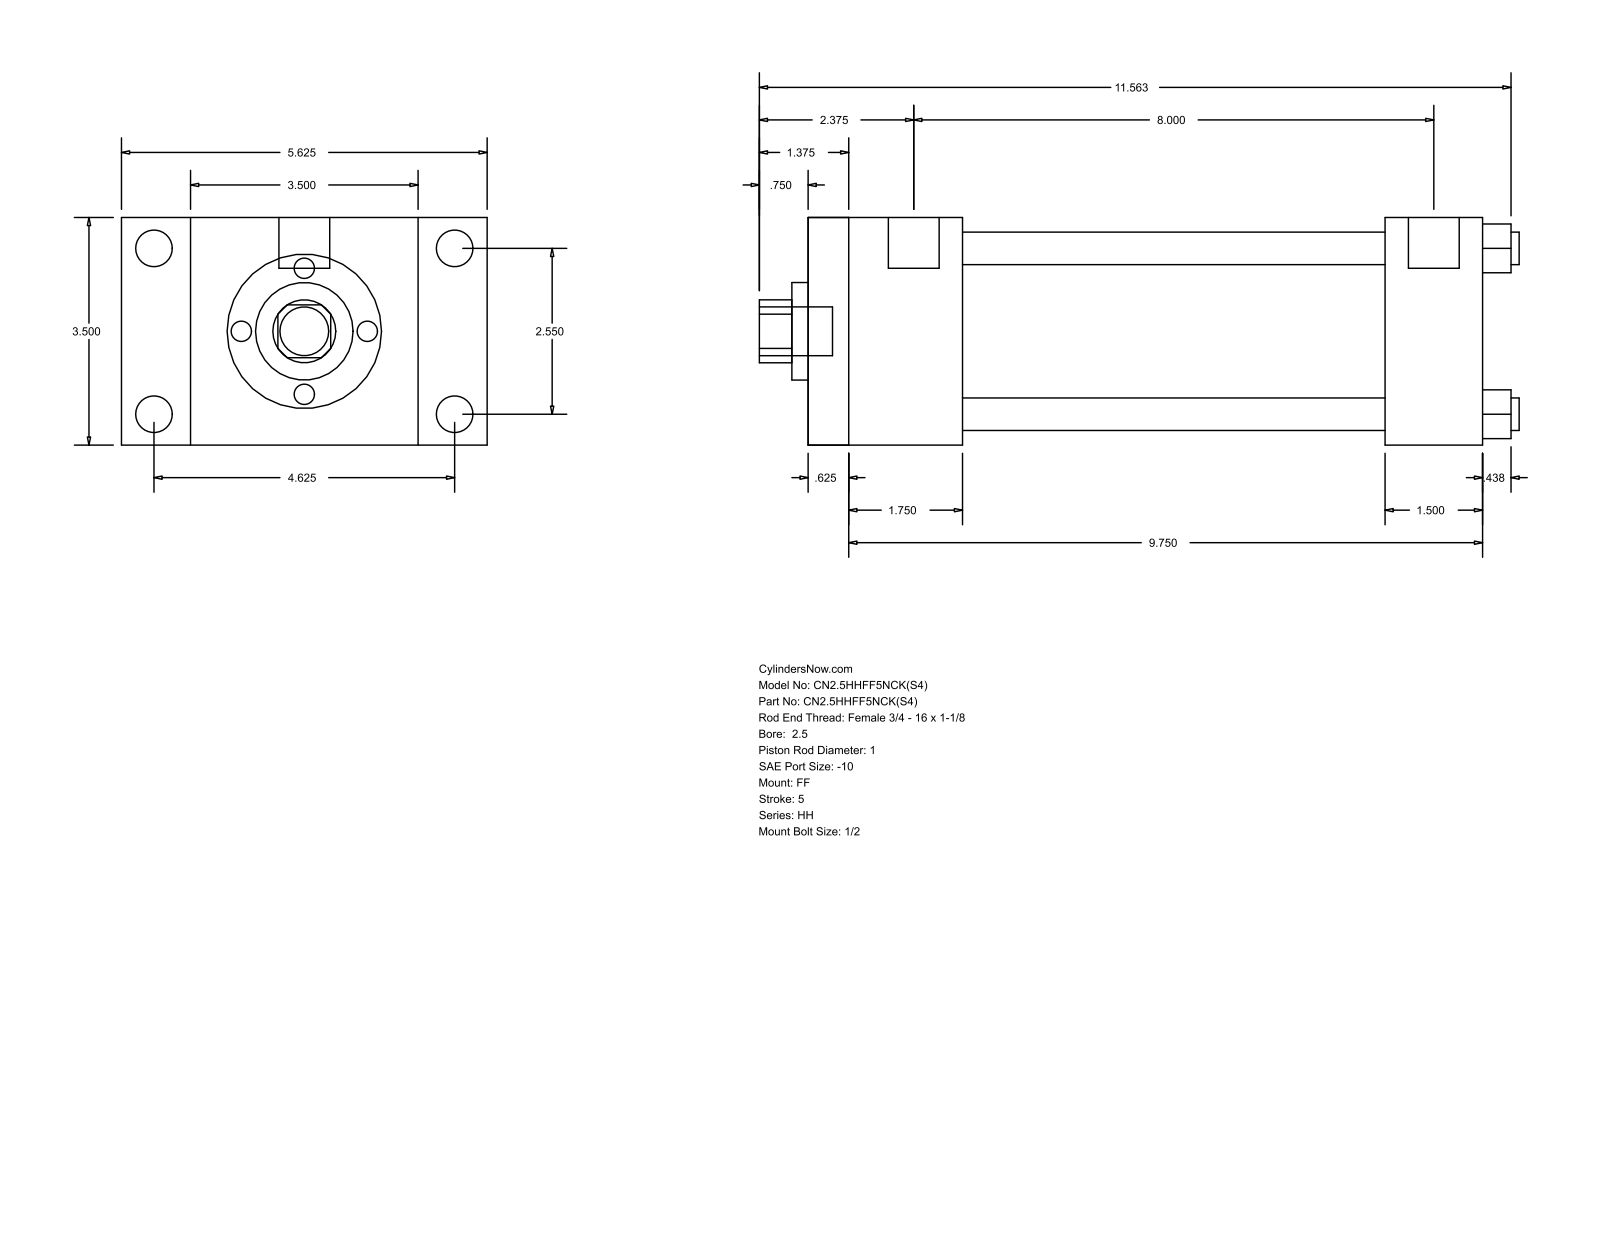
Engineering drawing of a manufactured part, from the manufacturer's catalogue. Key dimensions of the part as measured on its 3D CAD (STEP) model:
Part name (STEP PRODUCT): HH_FF__0250_1
STEP written by: GSSL Pune (CONFIG_CONTROL_DESIGN)
Units: millimetres
Bodies: 0 solids, 92 faces (64 planar, 28 cylindrical, 0 other)
Overall size (bounding box): 296.86 × 142.88 × 88.9
Round holes (diameter × count): ⌀12.7 ×4, ⌀25.4 ×1, ⌀38.1 ×1, ⌀73.03 ×1
Round bosses / shafts (diameter × count): ⌀14.3 ×4, ⌀5.56 ×4, ⌀19.84 ×2, ⌀19.05 ×1
Partial cylindrical surfaces — rounded edges, fillets, slot ends (radius × count): R12.29 ×1
Main face-to-face distances: 88.9, 263.52, 15.87, 247.65, 60.33, 44.46, 203.19, 225.42, 209.55, 165.09
Hole centre spacings: 45.79, 64.76, 91.58
